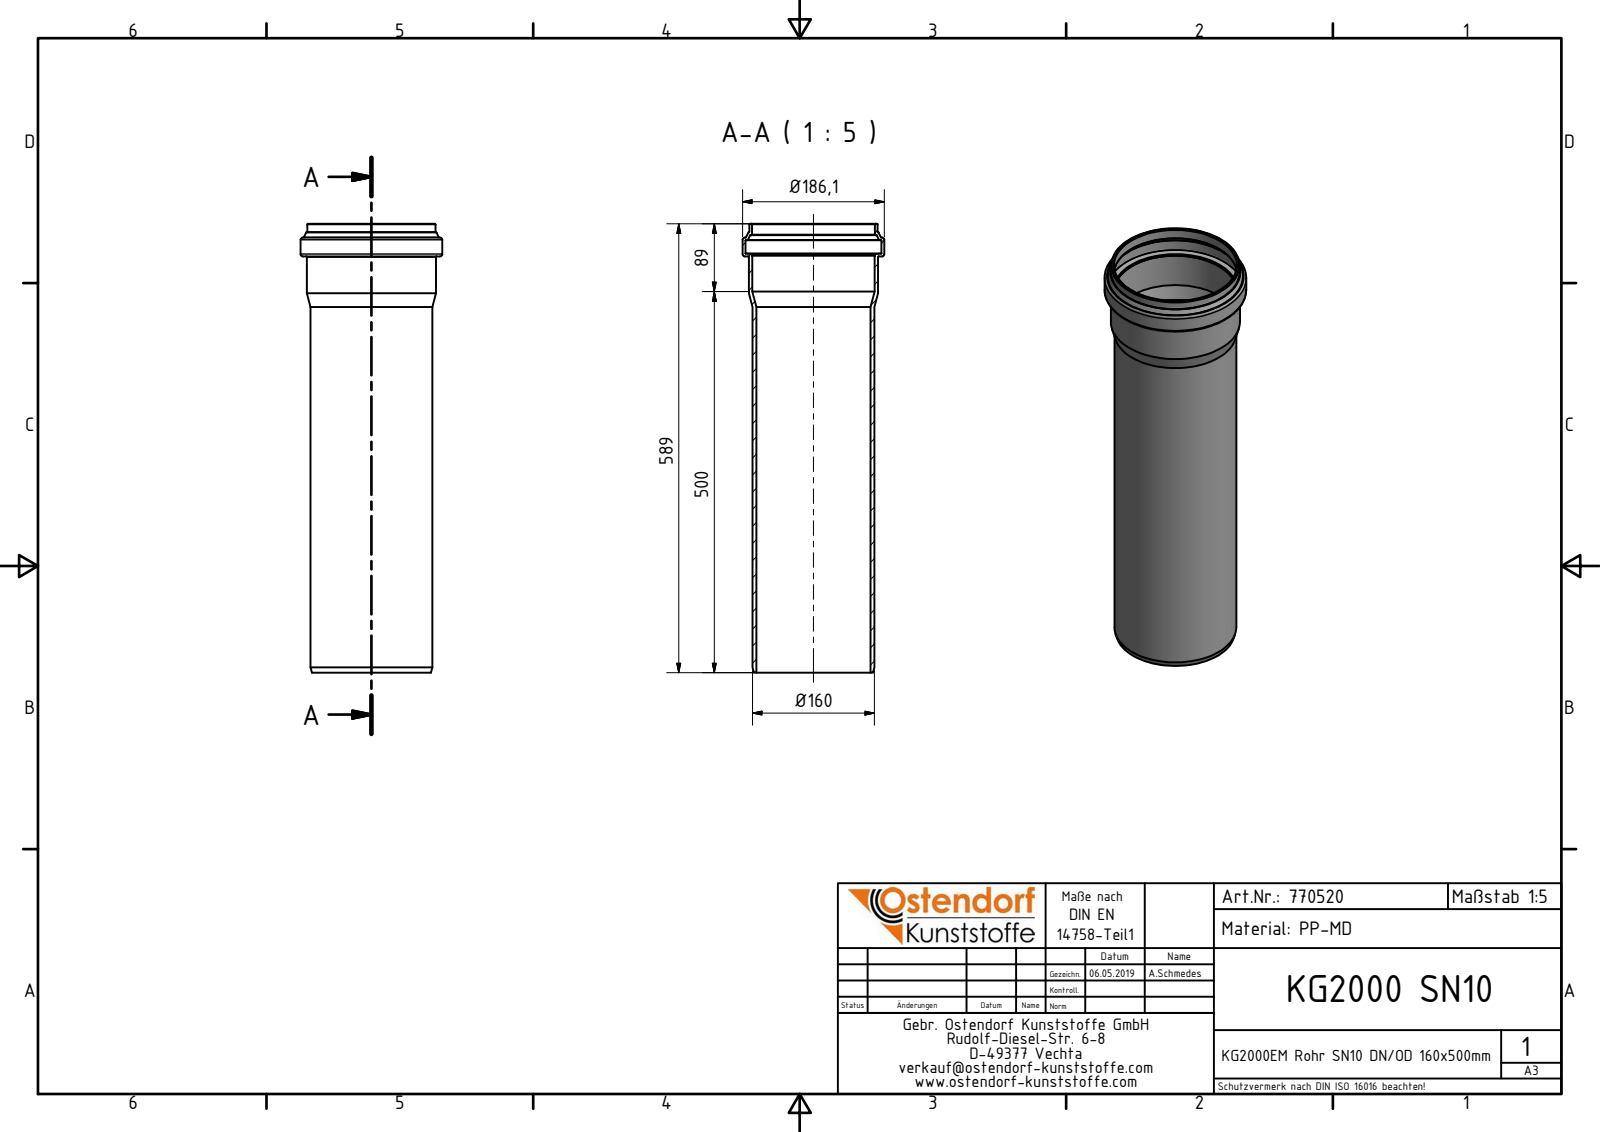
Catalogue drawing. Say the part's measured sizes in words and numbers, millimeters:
The part is named "770520 KG2000EM Rohr SN10 DN-OD160x500". Its 3-D file was written by "Autodesk Inventor 2016 (AUTOMOTIVE_DESIGN)". It is 1 solid with 37 faces: 6 planar, 9 cylindrical and 22 other. Overall it measures 589 by 186.1 by 186.1 millimeters. Its volume is 1 454 000 cubic millimeters and its surface area 599 479 square millimeters. Round holes: 1 of diameter 149.85, 1 of diameter 160.6, 1 of diameter 161, 1 of diameter 178.7. Round bosses or shafts: 1 of diameter 186.1, 1 of diameter 169.6, 1 of diameter 168.4, 1 of diameter 160. The main face-to-face distances are 546.3, 589, 42.7, 571, 24.7, 18, 577.91, 31.61, 6.91, 11.09.
